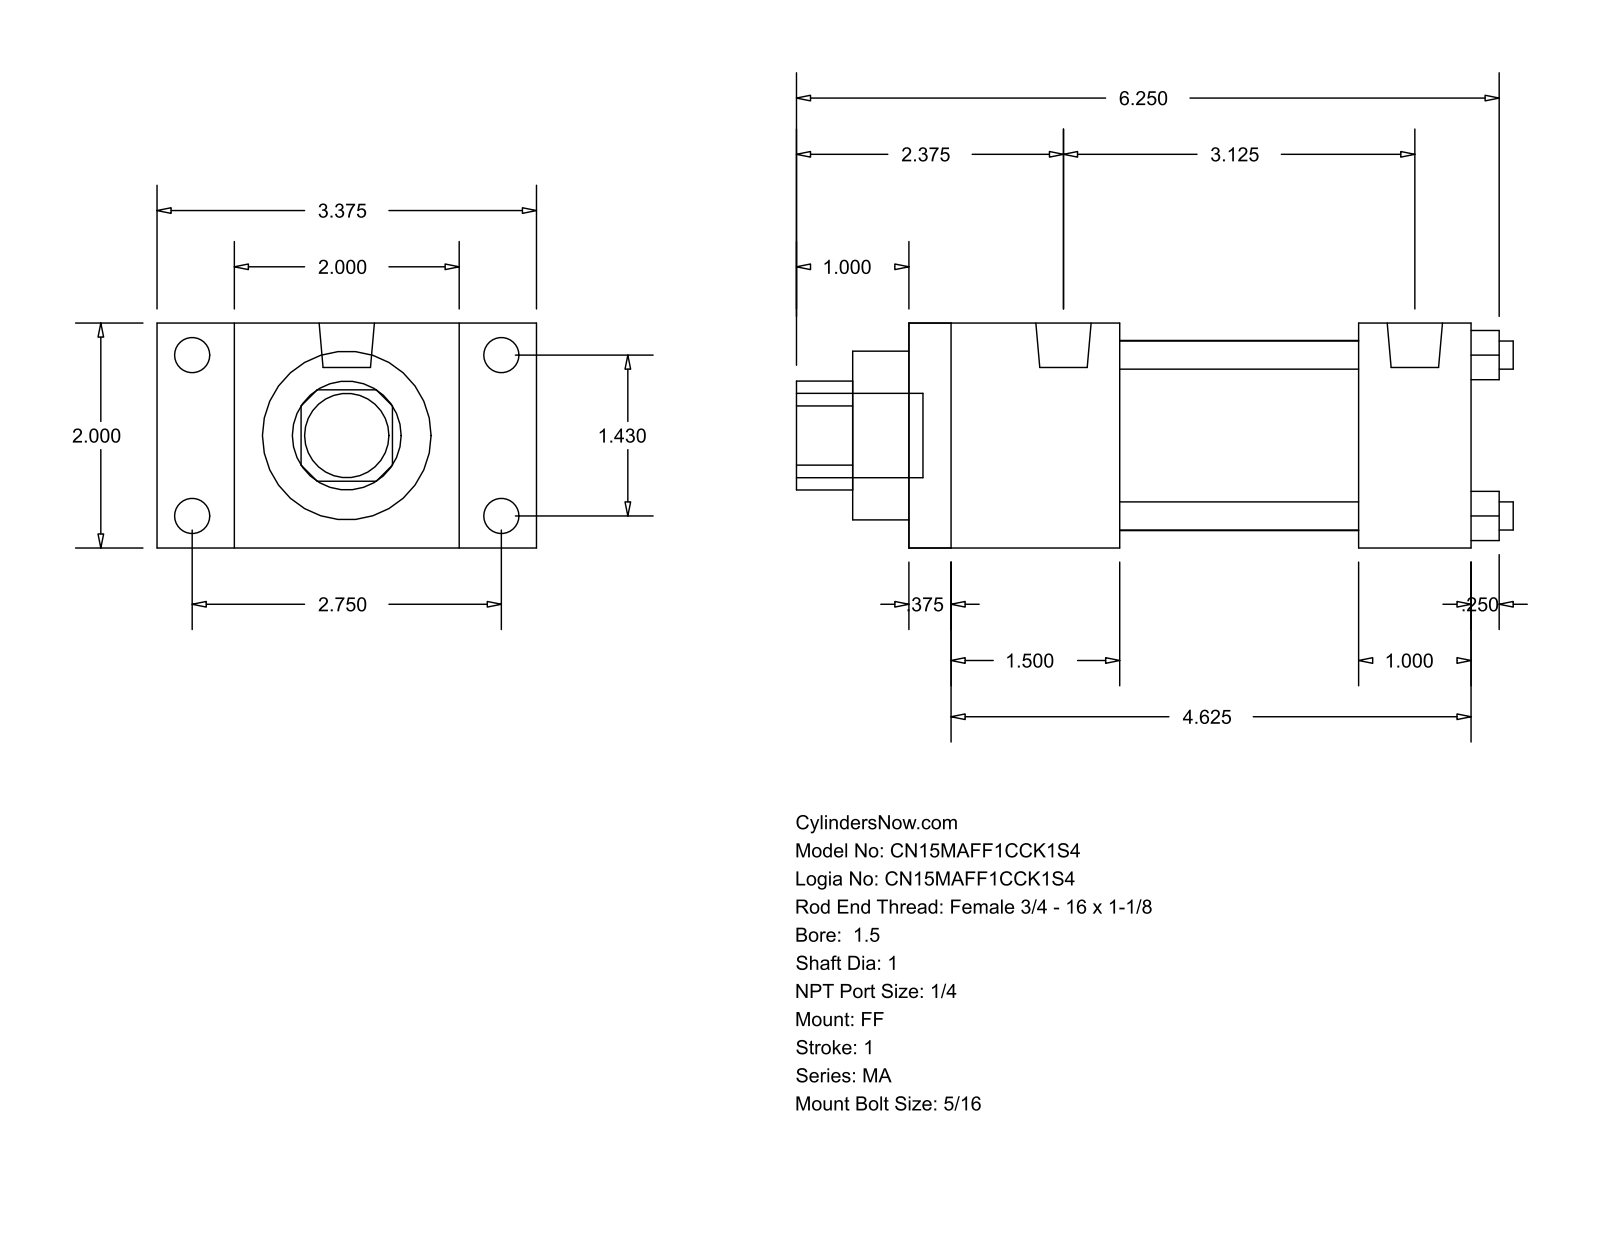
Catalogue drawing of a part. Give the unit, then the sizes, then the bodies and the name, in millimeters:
Units: millimetres
Overall size (bounding box): 161.93 × 85.72 × 50.8
Round holes (diameter × count): ⌀6.35 ×4, ⌀25.4 ×1, ⌀38.1 ×1, ⌀42.93 ×1
Round bosses / shafts (diameter × count): ⌀7.94 ×8, ⌀12.49 ×2, ⌀19.05 ×1
Partial cylindrical surfaces — rounded edges, fillets, slot ends (radius × count): R12.29 ×1
Main face-to-face distances: 50.8, 127, 9.52, 117.48, 25.4, 47.63, 101.6, 38.11, 92.08, 53.97
Hole centre spacings: 25.68, 36.32, 51.36
Bodies: 0 solids, 92 faces (64 planar, 28 cylindrical, 0 other)
Part name (STEP PRODUCT): MA_FF__0150_1
STEP written by: GSSL Pune (CONFIG_CONTROL_DESIGN)
